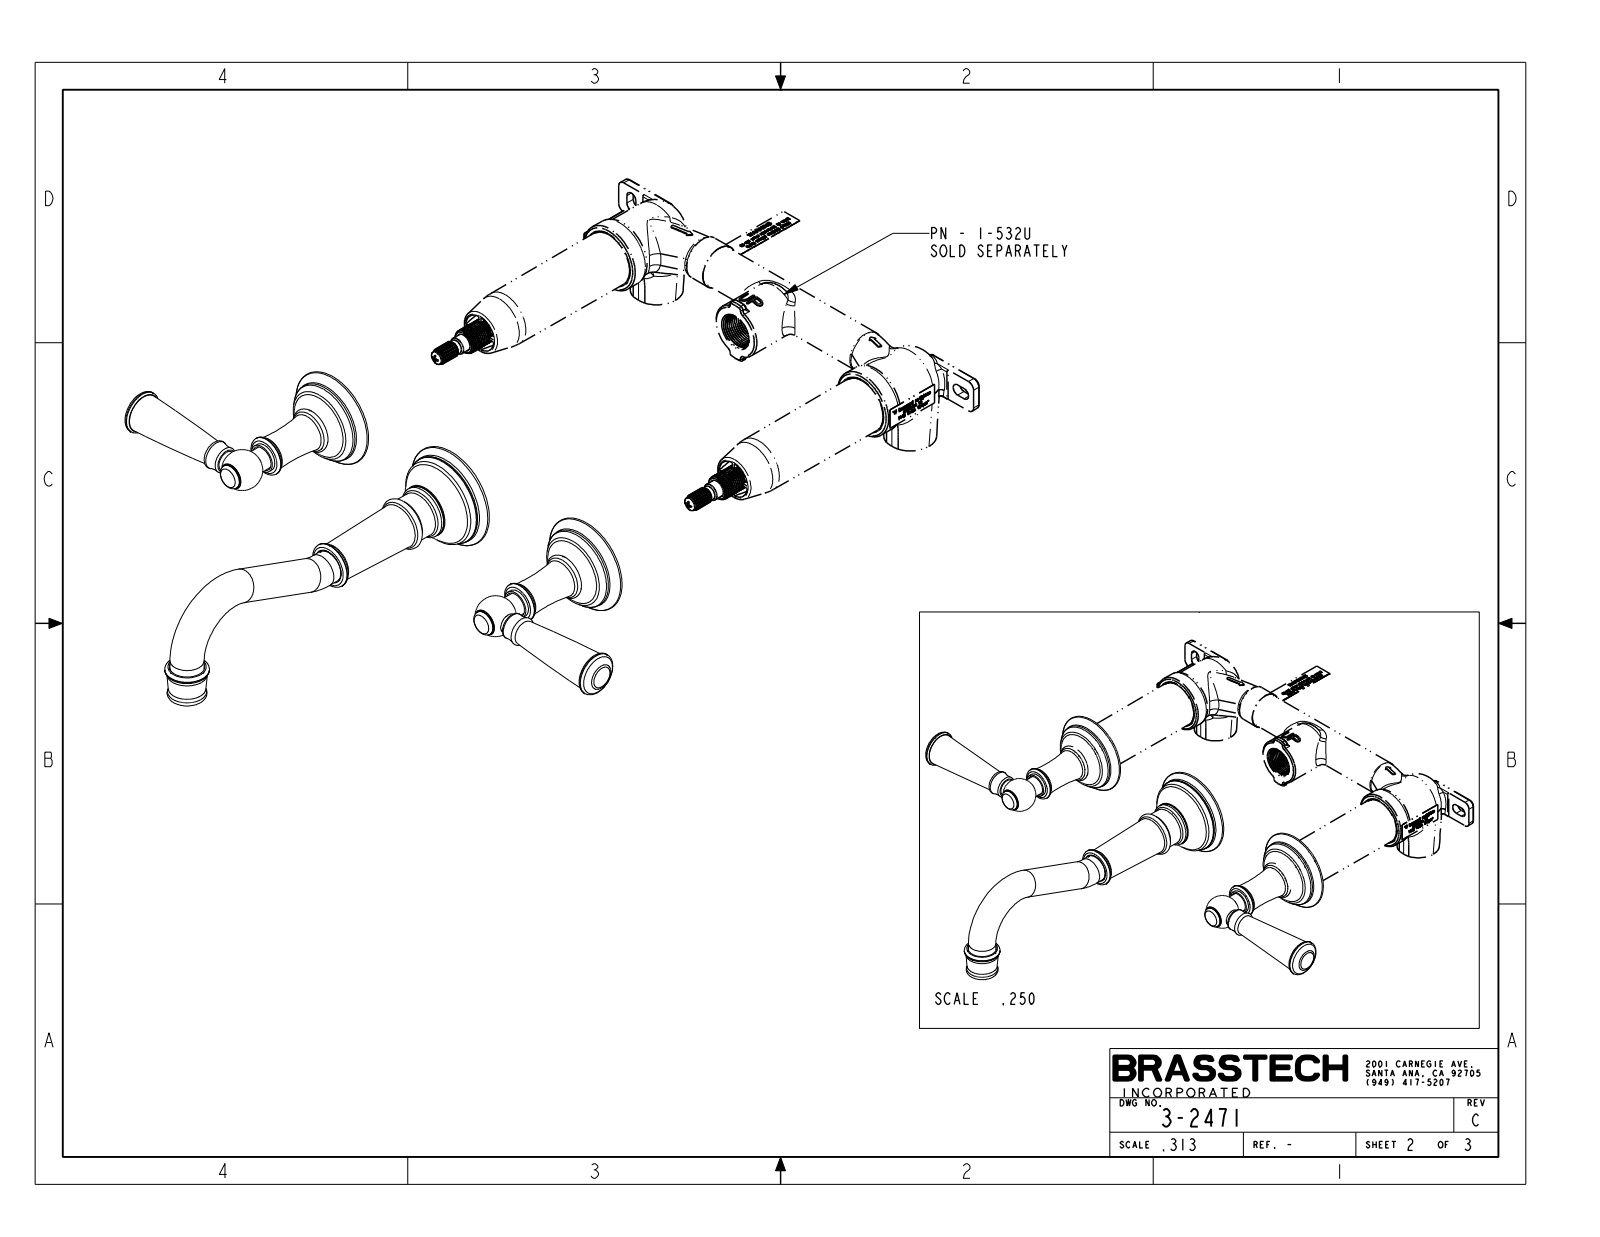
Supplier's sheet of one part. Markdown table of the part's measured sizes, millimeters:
| quantity | value |
| --- | --- |
| part name | 3-2471_SW0001 |
| STEP written by | CREO PARAMETRIC BY PTC INC, 2018400 (AUTOMOTIVE_DESIGN) |
| units | millimeters |
| bodies | 3 solids, 219 faces (23 planar, 38 cylindrical, 158 other) |
| overall size | 367.7 × 221.2 × 65 |
| volume | 256 300 mm³ |
| surface area | 53 550 mm² |
| round bosses / shafts (diameter × count) | 19.1 × 3, 22.9 × 2, 16.5 × 2, 14.2 × 2, 13.1 × 2, 30.6 × 1, 26.4 × 1, 25 × 1 |
| main face-to-face distances | 54.4, 56.4, 2, 97.2, 42.9, 40.8, 367.7, 19.6, 80.5, 26.2 |
